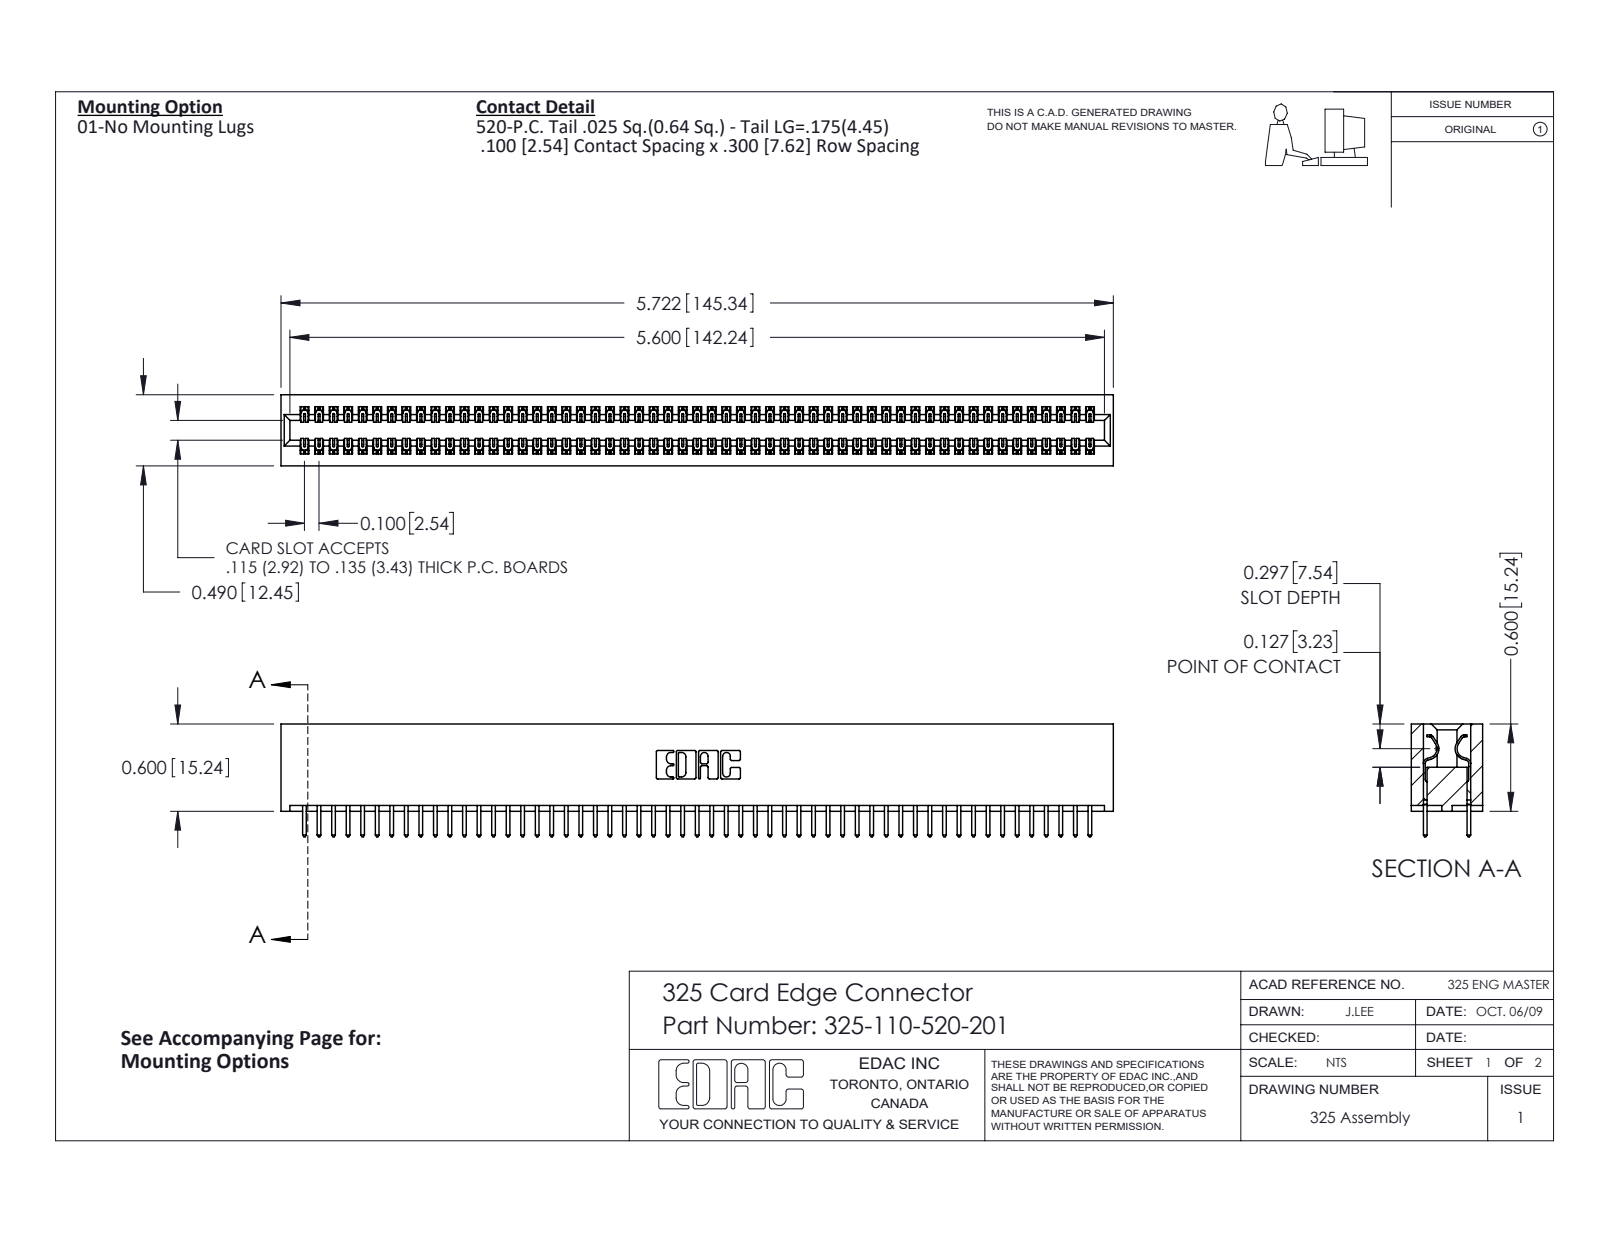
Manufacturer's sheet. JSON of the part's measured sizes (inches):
{"part_name": "325 Part_Lugless; 325-110-520-201; 325-292-001_325-293-120", "step_written_by": "SolidWorks 2016 (CONFIG_CONTROL_DESIGN)", "units": "inches", "bodies": {"solids": 111, "faces": 5826, "planar": 4026, "cylindrical": 1800, "other": 0}, "overall_size": [5.722, 0.775, 0.49], "volume_in3": 1.188, "surface_area_in2": 37.68, "partial_cylinders_radius": [[0.006, 165], [0.01, 110], [0.01, 22], [0.007, 6], [0.031, 6], [0.026, 3], [0.014, 2], [0.022, 2]], "face_to_face_distances": [0.083, 0.407, 0.3, 0.49, 0.107, 0.383, 0.025, 0.325, 0.275, 0.263]}
